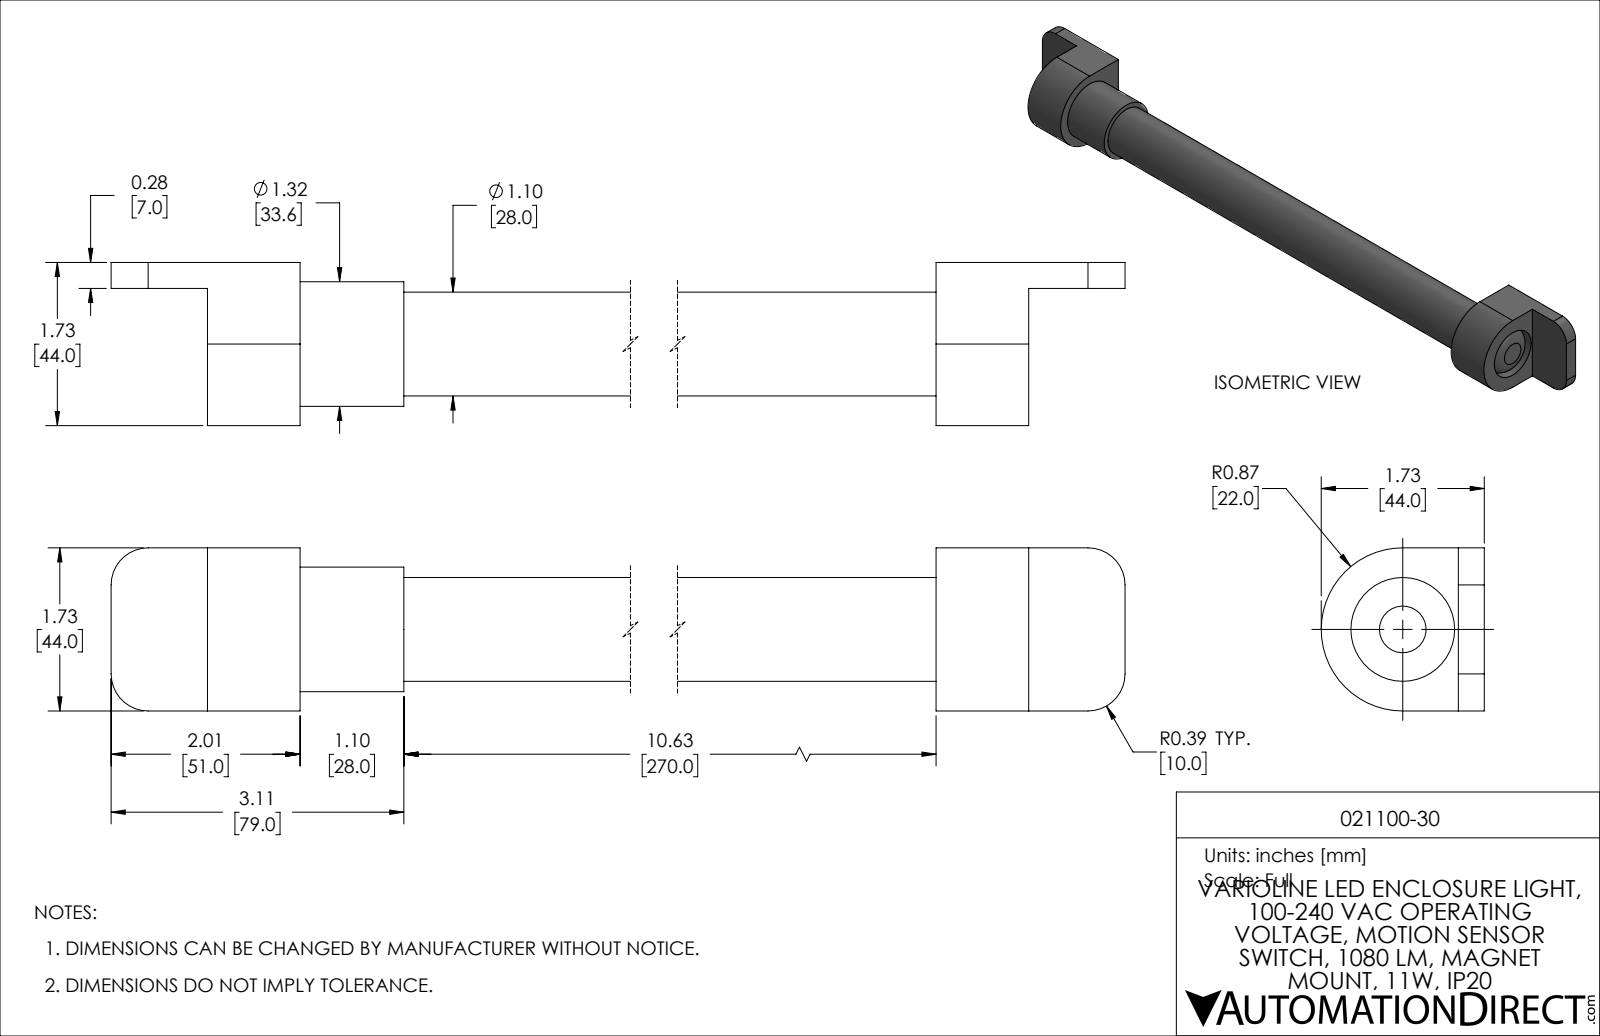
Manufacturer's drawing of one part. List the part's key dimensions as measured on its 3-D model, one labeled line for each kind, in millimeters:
Part name (STEP PRODUCT): PRODUCT_NAME_1
STEP written by: ACIS (AUTOMOTIVE_DESIGN_CC2)
Units: millimetres
Bodies: 1 solid, 35 faces (17 planar, 14 cylindrical, 4 other)
Overall size (bounding box): 400 × 44 × 44
Volume: 290 937 mm³ · Surface area: 47 331 mm²
Round holes (diameter × count): ⌀28 ×1
Round bosses / shafts (diameter × count): ⌀33.6 ×1
Partial cylindrical surfaces — rounded edges, fillets, slot ends (radius × count): R10 ×4, R22 ×1
Main face-to-face distances: 7, 25, 323, 44, 348, 298, 26, 51, 349, 374
